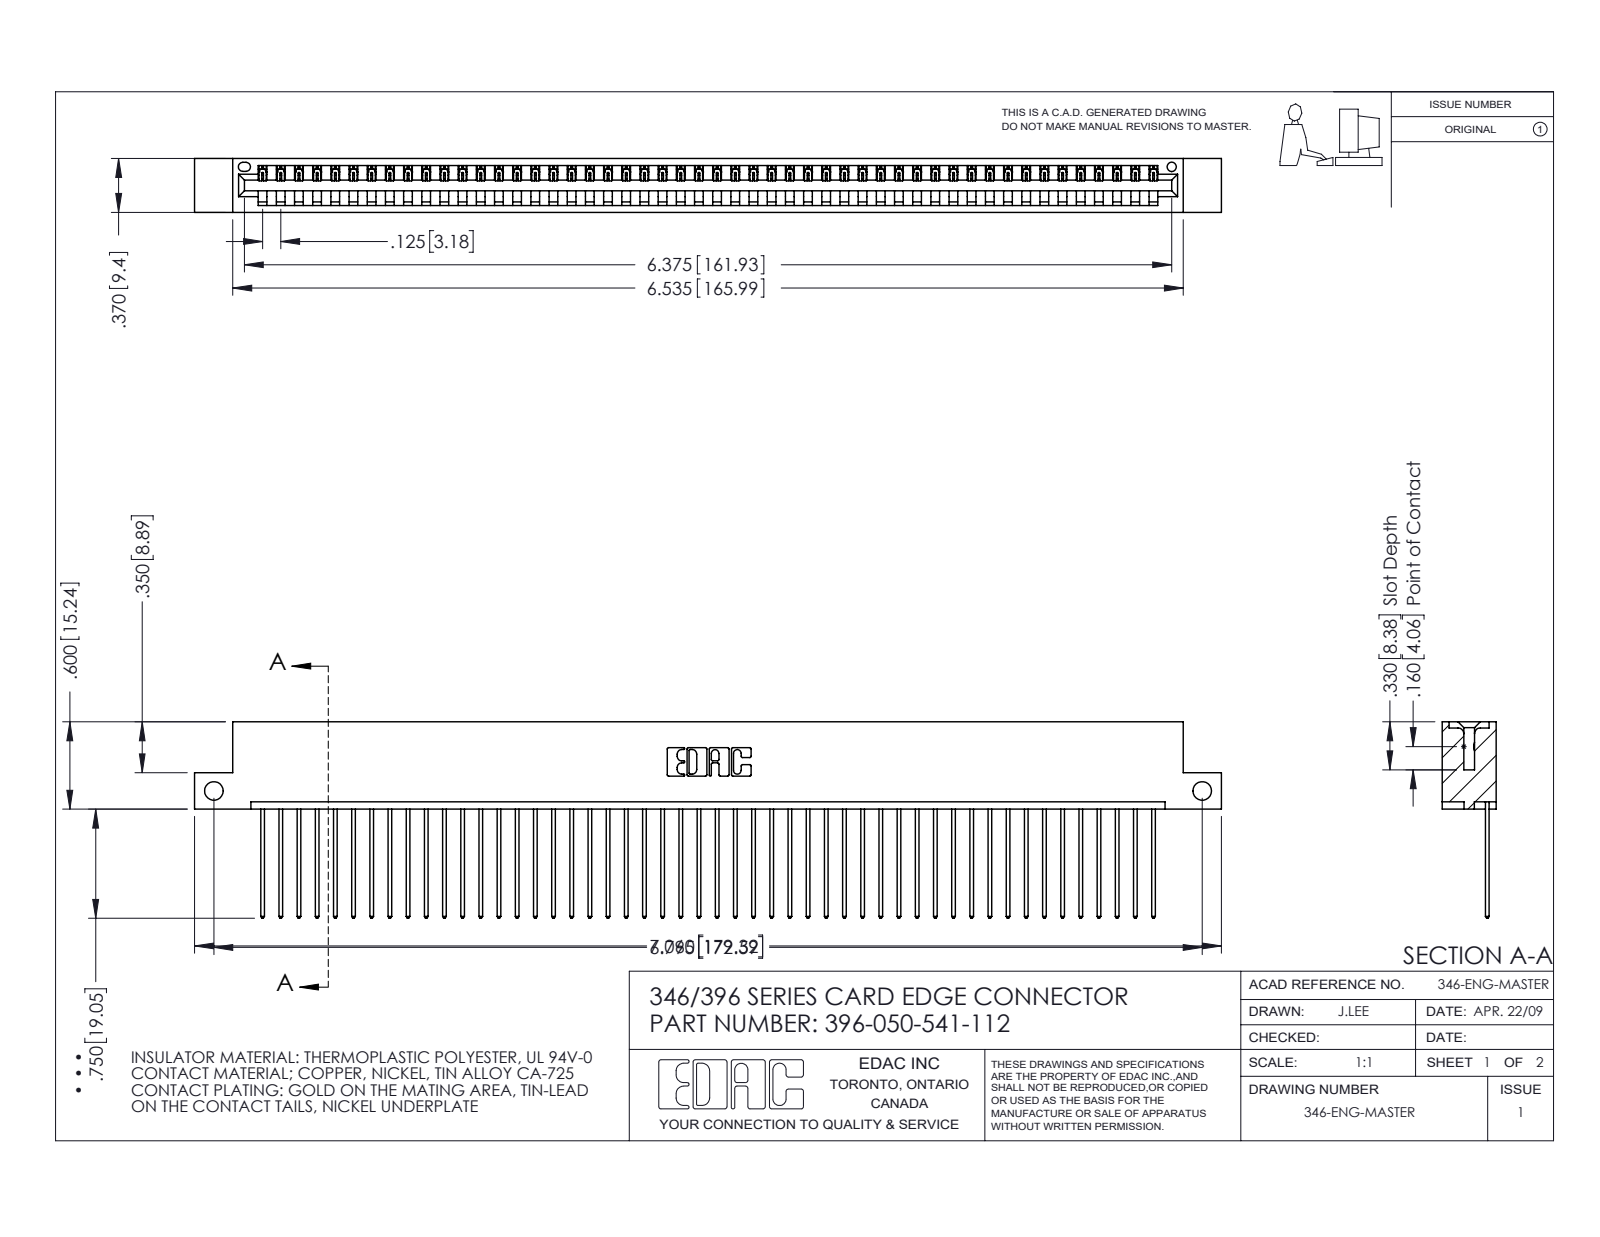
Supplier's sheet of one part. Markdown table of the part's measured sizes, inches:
| quantity | value |
| --- | --- |
| part name | 346 Part_Flush Mounting Lugs - Side Mount; 396-050-541-112; 345-292-001_345-293-141 |
| STEP written by | SolidWorks 2016 (CONFIG_CONTROL_DESIGN) |
| units | inches |
| bodies | 51 solids, 3022 faces (2076 planar, 946 cylindrical, 0 other) |
| overall size | 7.06 × 1.35 × 0.37 |
| volume | 1.056 in³ |
| surface area | 34.95 in² |
| round holes (diameter × count) | 0.128 × 2, 0.064 × 1 |
| partial cylindrical surfaces (radius × count) | 0.006 × 100, 0.01 × 100, 0.01 × 22, 0.007 × 6, 0.031 × 6, 0.026 × 3, 0.031 × 2, 0.04 × 2 |
| main face-to-face distances | 0.048, 0.322, 0.37, 0.25, 0.072, 0.298, 0.025, 0.148, 0.222, 0.1 |
| hole center spacings | 6.795 |
